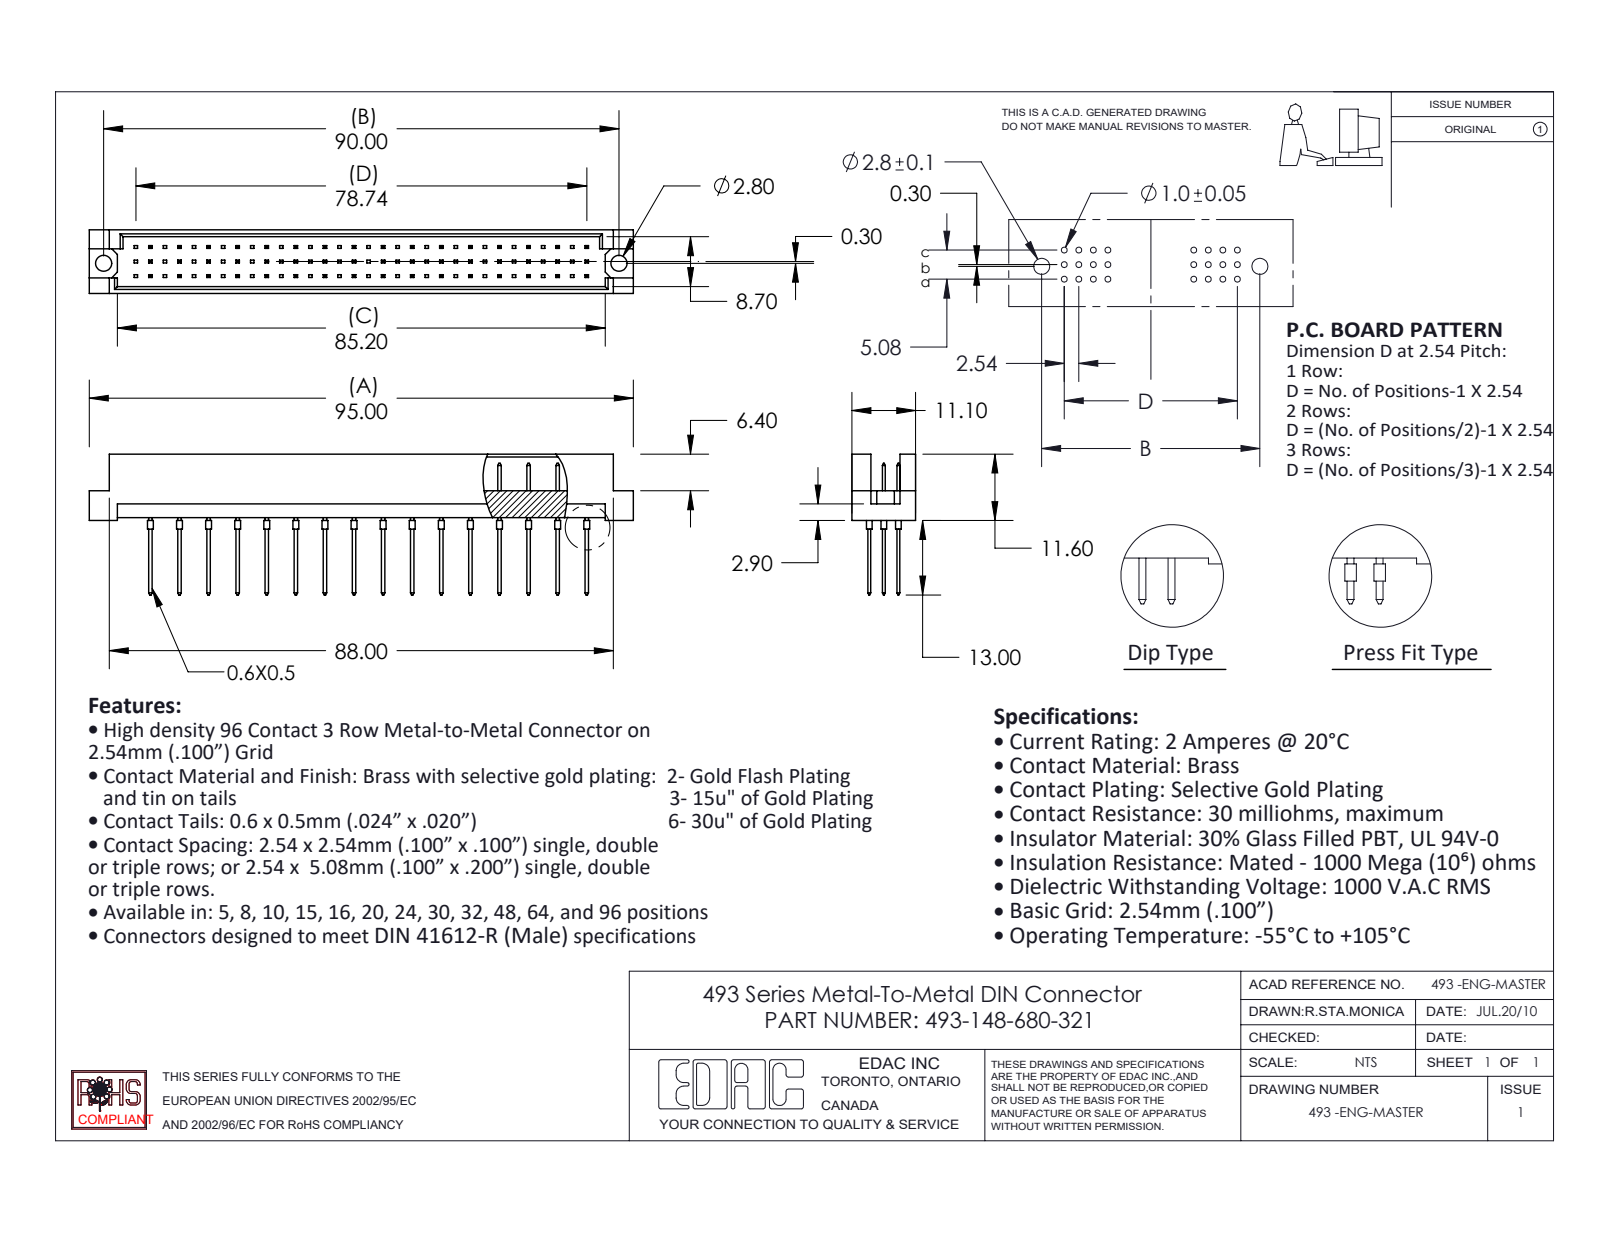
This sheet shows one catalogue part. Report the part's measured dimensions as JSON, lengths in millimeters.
{"part_name": "493 Part_96; 493-148-680-321; 493-290_80", "step_written_by": "SolidWorks 2020 (CONFIG_CONTROL_DESIGN)", "units": "millimeters", "bodies": {"solids": 49, "faces": 1492, "planar": 1392, "cylindrical": 100, "other": 0}, "overall_size": [95, 24.6, 11.1], "volume_mm3": 6020, "surface_area_mm2": 8999, "round_holes": [[2.8, 2]], "round_bosses_or_shafts": [[1, 48]], "face_to_face_distances": [1.2, 9.9, 5.08, 2.54, 0.5, 11.1, 8.7, 4.7, 2.76, 3.26], "hole_center_spacings": [90]}
